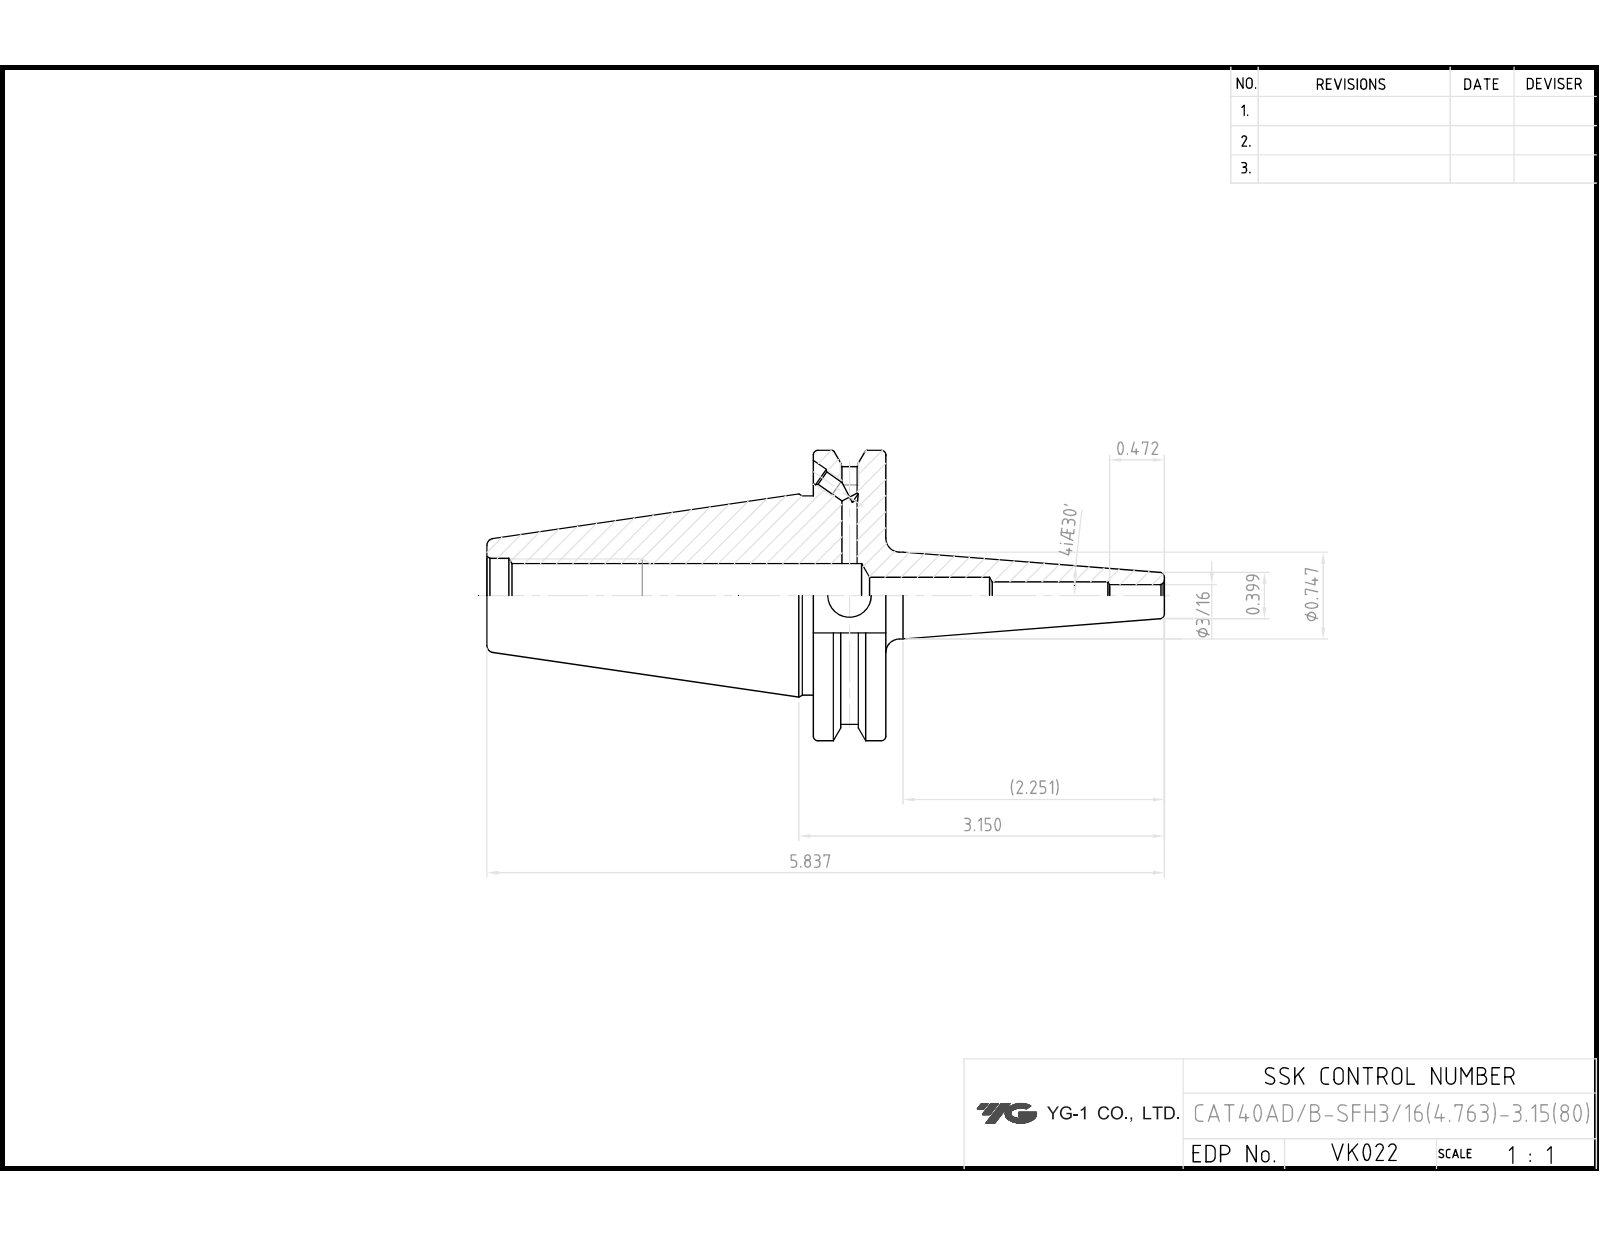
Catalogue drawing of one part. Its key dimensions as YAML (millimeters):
part_name: "LO-CAT40ADB-SFH4.7625-80"
step_written_by: "Autodesk Inventor 2024 (AUTOMOTIVE_DESIGN)"
units: millimeters
bodies: {solids: 1, faces: 87, planar: 35, cylindrical: 29, other: 23}
overall_size: [148.25, 63.5, 61.09]
volume: 109982
surface_area: 24542
round_holes:
  - {diameter: 3.24, count: 4}
  - {diameter: 4, count: 2}
  - {diameter: 4.2, count: 2}
  - {diameter: 4.76, count: 1}
  - {diameter: 6, count: 1}
  - {diameter: 8, count: 1}
  - {diameter: 9.53, count: 1}
  - {diameter: 13, count: 1}
  - {diameter: 13.39, count: 1}
  - {diameter: 16.3, count: 1}
round_bosses_or_shafts:
  - {diameter: 63.5, count: 1}
  - {diameter: 43.6, count: 1}
  - {diameter: 19, count: 1}
partial_cylinders:
  - {radius: 28.15, count: 1}
face_to_face_distances: [15.88, 47.6, 16.38, 71.42, 87.3, 77.47, 6.05, 9.83, 81.3, 9.88]
